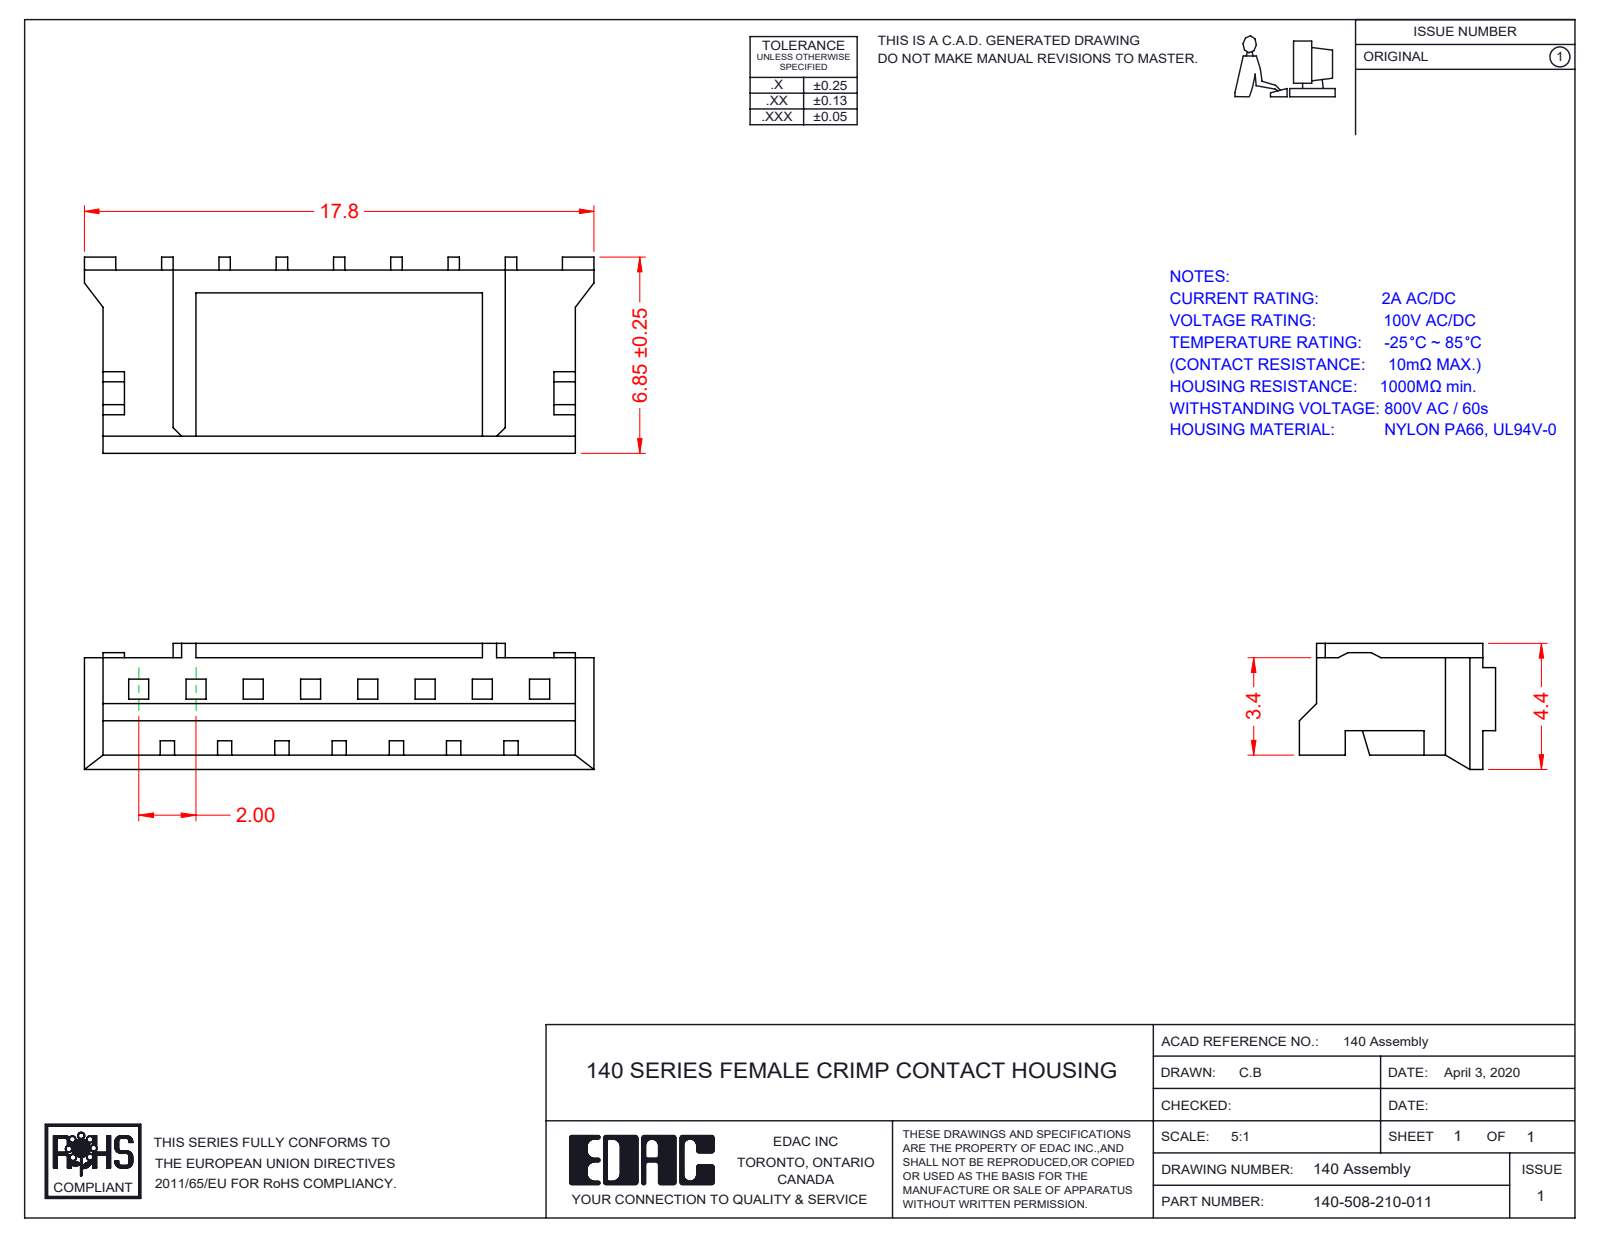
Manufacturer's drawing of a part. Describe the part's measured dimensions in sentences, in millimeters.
The part is named "140-508-210-011". Its 3-D file was written by "SolidWorks 2016 (CONFIG_CONTROL_DESIGN)". It is 1 solid with 260 faces: 260 planar, 0 cylindrical and 0 other. Overall it measures 17.8 by 6.85 by 4.4 millimeters. Its volume is 179 cubic millimeters and its surface area 794 square millimeters. The main face-to-face distances are 2, 4, 6, 1.6, 8, 0.4, 3.6, 5.6, 0.85, 10.
